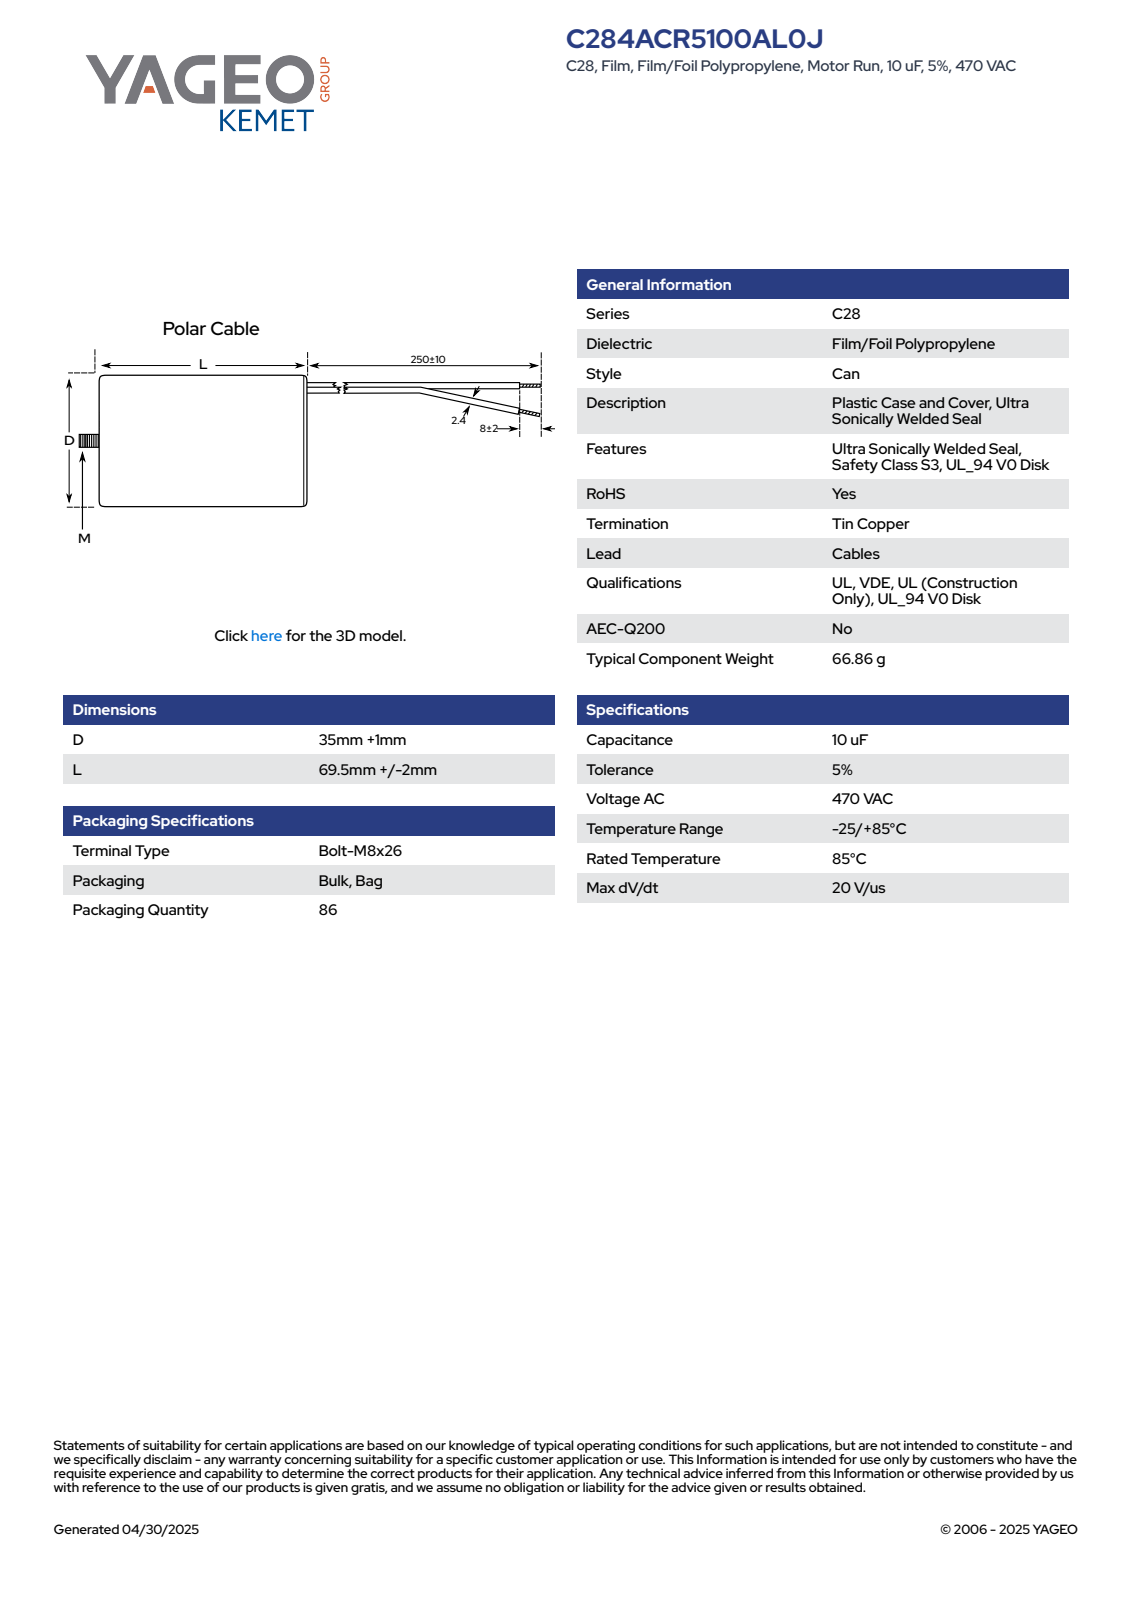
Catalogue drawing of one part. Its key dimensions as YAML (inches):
part_name: "CFM_KC28P_35X69.5_D36L71.5"
step_written_by: "SolidWorks 2014 (AUTOMOTIVE_DESIGN)"
units: inches
bodies: {solids: 1, faces: 76, planar: 26, cylindrical: 15, other: 35}
overall_size: [3.209, 1.418, 1.417]
volume: 4.371
surface_area: 16.24
round_holes:
  - {diameter: 1.26, count: 1}
round_bosses_or_shafts:
  - {diameter: 1.417, count: 1}
  - {diameter: 0.315, count: 1}
partial_cylinders:
  - {radius: 0.709, count: 1}
face_to_face_distances: [2.736, 2.815, 0.079, 0.394, 3.13, 3.209]
